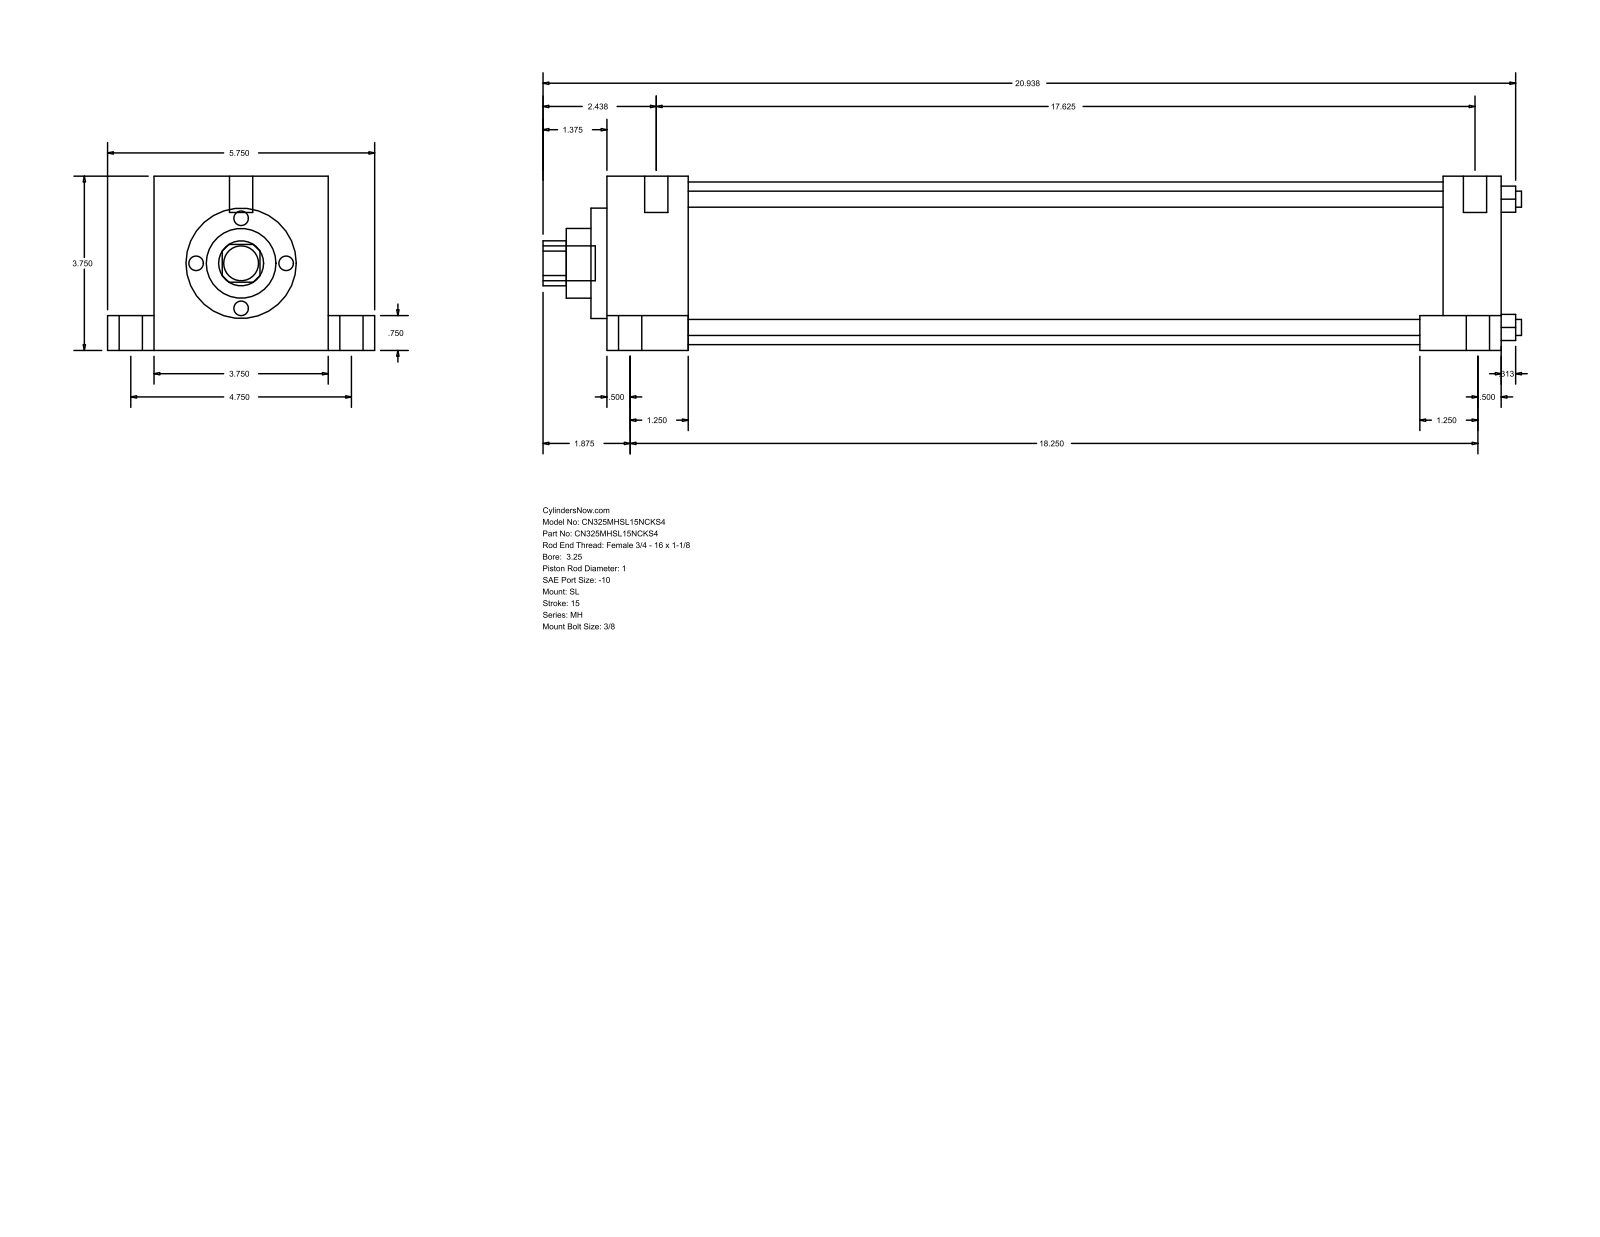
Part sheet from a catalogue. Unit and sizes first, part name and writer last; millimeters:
Units: millimetres
Overall size (bounding box): 534.99 × 146.05 × 95.25
Round holes (diameter × count): ⌀8.76 ×4, ⌀25.4 ×1, ⌀38.1 ×1, ⌀60.33 ×1, ⌀88.9 ×1
Round bosses / shafts (diameter × count): ⌀12.7 ×6, ⌀19.05 ×5, ⌀5.56 ×4
Partial cylindrical surfaces — rounded edges, fillets, slot ends (radius × count): R12.29 ×1
Main face-to-face distances: 95.24, 488.96, 44.46, 444.5, 25.41, 120.65, 19.05, 76.19, 457.2, 412.74
Hole centre spacings: 49.57, 70.1, 99.14
Bodies: 0 solids, 110 faces (77 planar, 33 cylindrical, 0 other)
Part name (STEP PRODUCT): MH_SL__0325_1
STEP written by: GSSL Pune (CONFIG_CONTROL_DESIGN)
